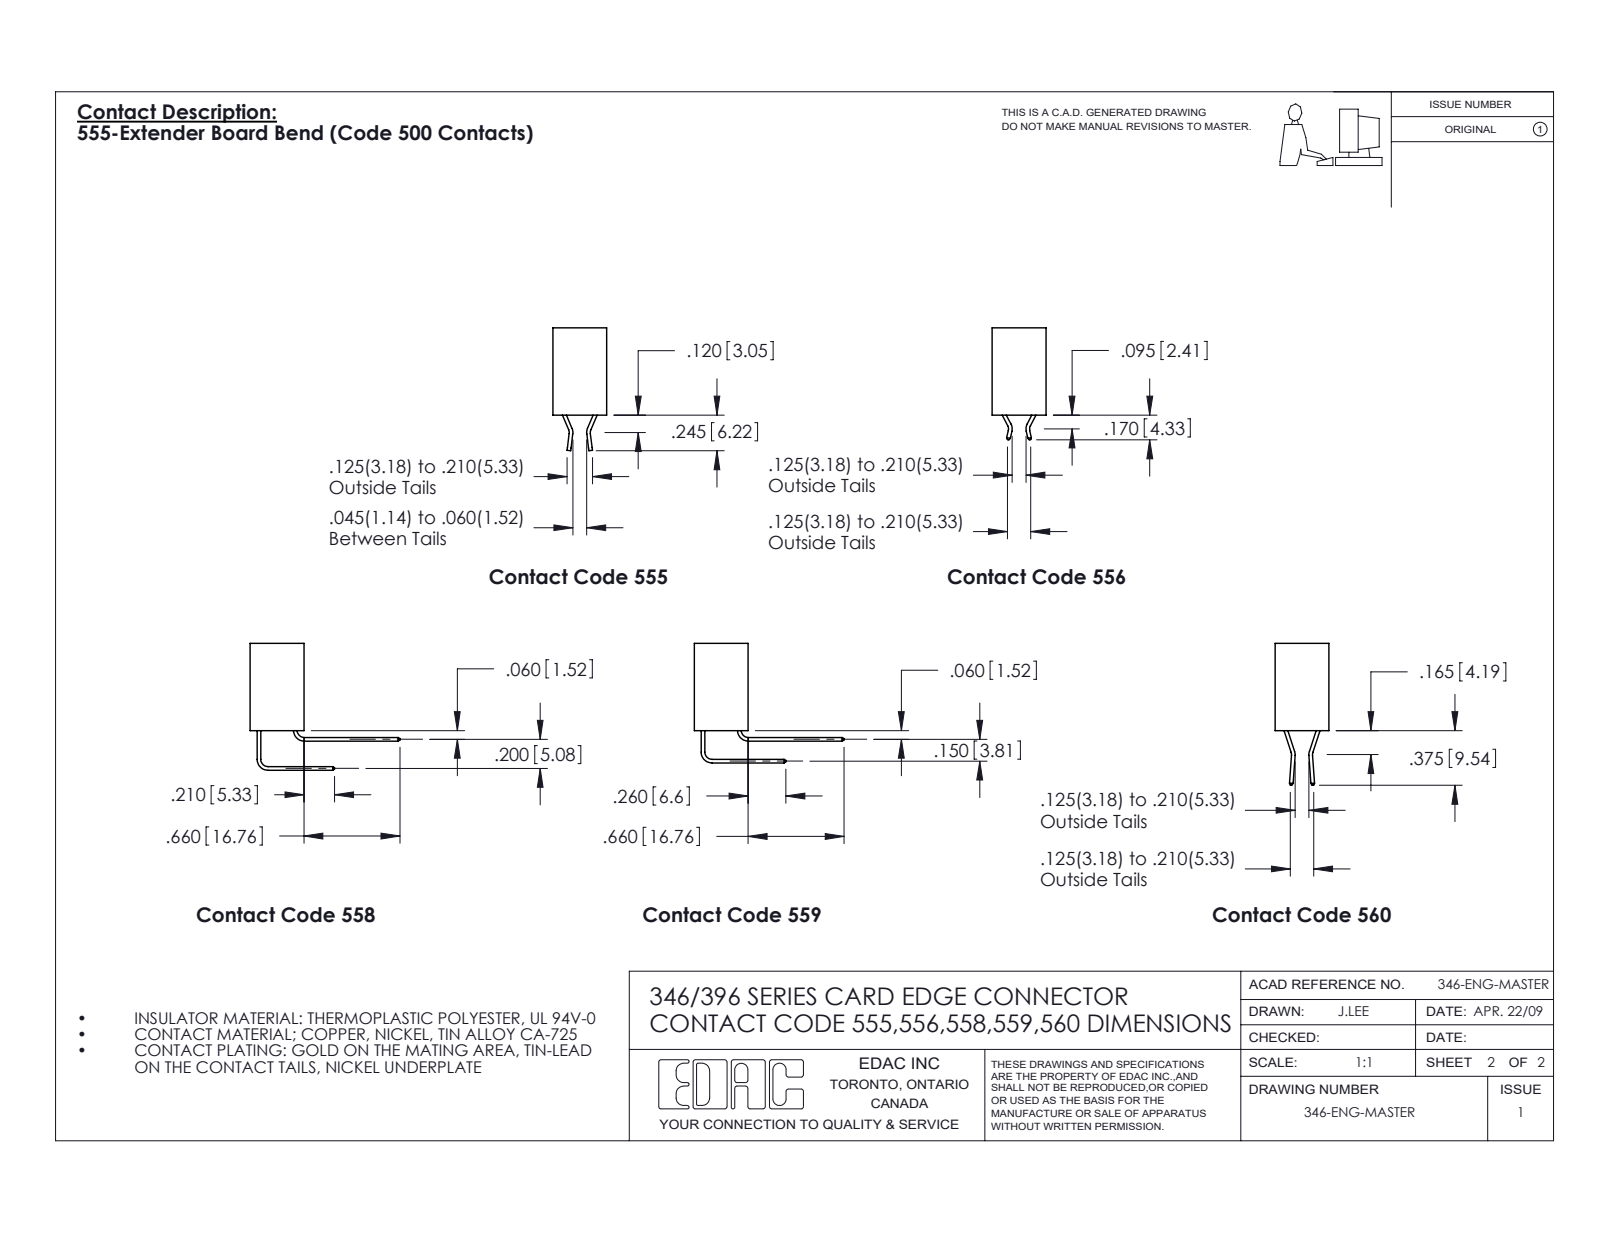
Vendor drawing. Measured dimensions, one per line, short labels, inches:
name: 396-068-560-201; 346 Part_No Mounting Lugs; 345-292-001_560 Tail
written by: SolidWorks 2016 (CONFIG_CONTROL_DESIGN)
unit: in
bodies: 69 solids, 3786 faces (2452 planar, 1334 cylindrical, 0 other)
size: 4.535 × 0.975 × 0.37
volume: 0.744 in³; area: 27.87 in²
holes: 1× ⌀0.064
rounds: 102× R0.006, 22× R0.01, 6× R0.007, 6× R0.031, 3× R0.026, 2× R0.01, 2× R0.014, 2× R0.022
face distances: 0.048, 0.322, 0.37, 0.025, 0.25, 0.072, 0.298, 0.275, 0.148, 0.222
